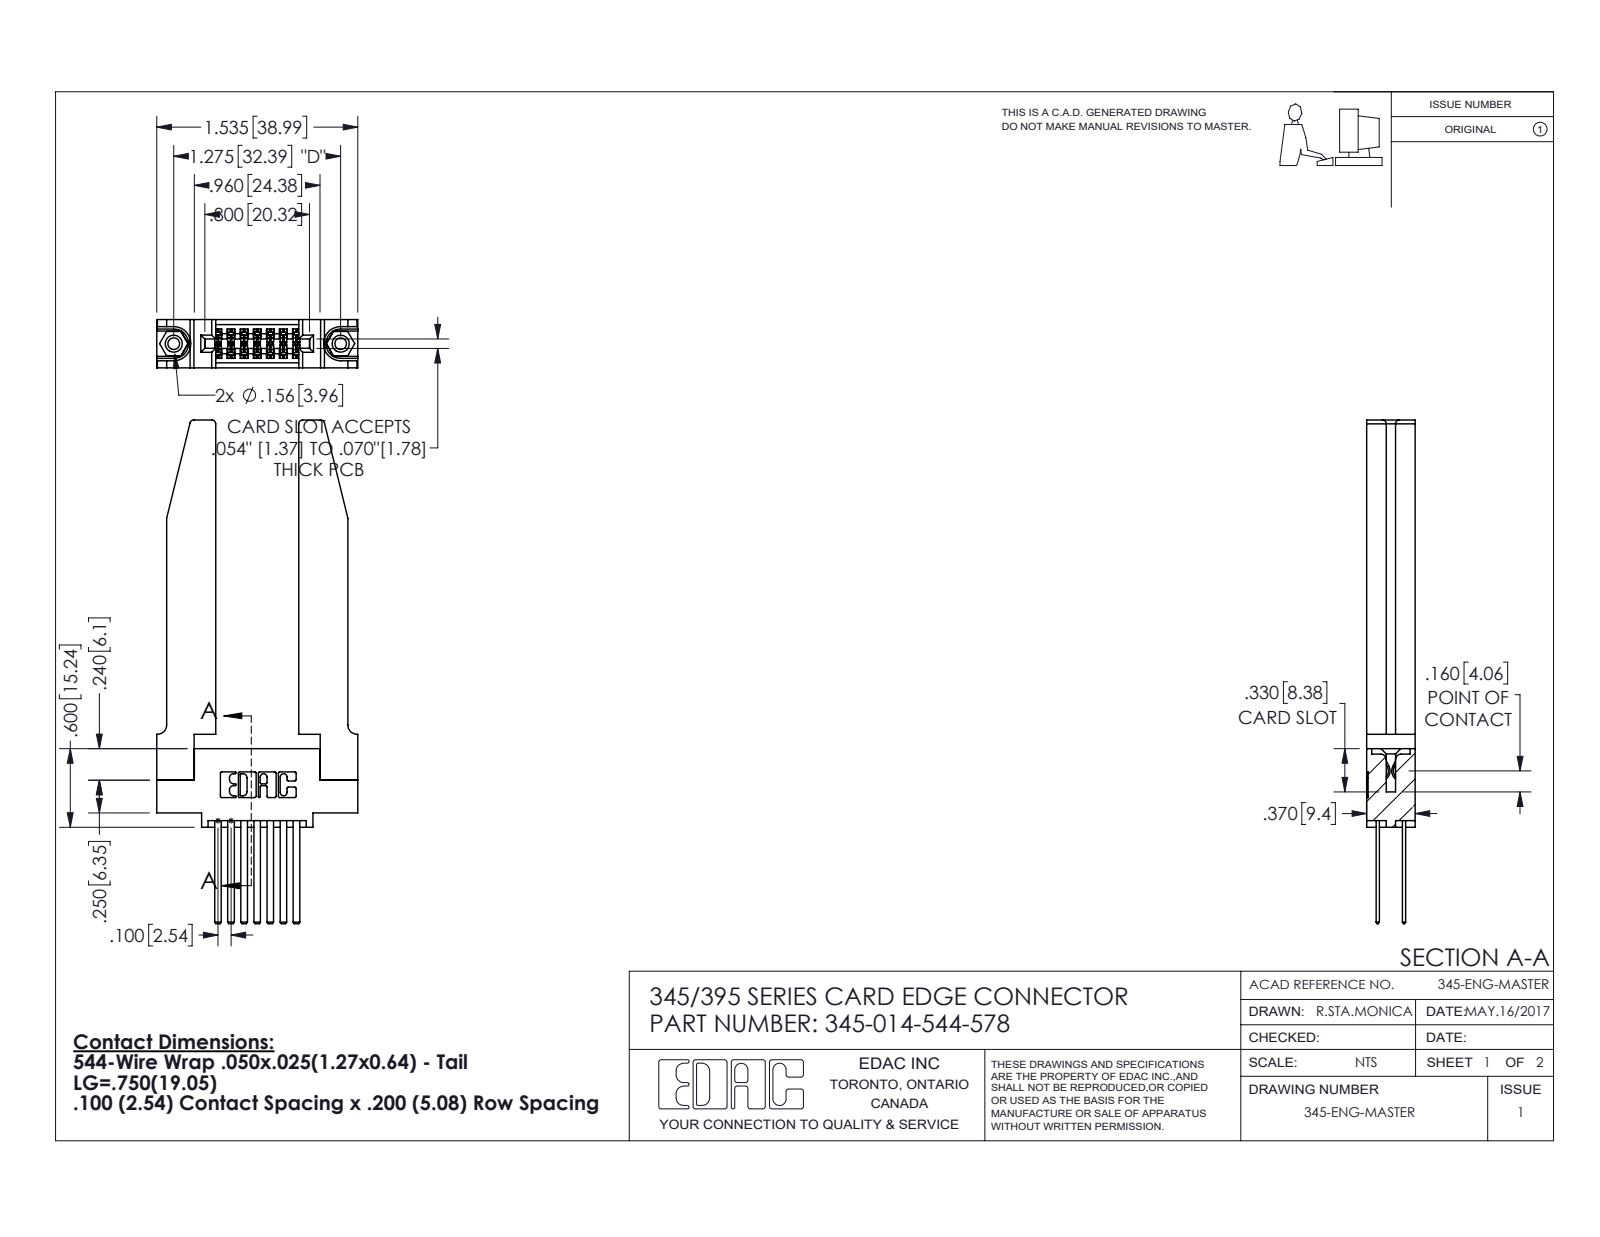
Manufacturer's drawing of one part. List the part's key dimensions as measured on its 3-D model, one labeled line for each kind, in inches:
Part name (STEP PRODUCT): 345-250-001_345-250-001-102; 345 Part_0.110 Offset - 0.156 Dia-TH; 345-014-544-578; 345-220-078_345-220-078 (+1 more)
STEP written by: SolidWorks 2016 (CONFIG_CONTROL_DESIGN)
Units: inches
Bodies: 19 solids, 980 faces (632 planar, 296 cylindrical, 52 other)
Overall size (bounding box): 3.847 × 1.536 × 0.37
Volume: 0.693 in³ · Surface area: 18.8 in²
Round holes (diameter × count): ⌀0.089 ×2, ⌀0.125 ×2, ⌀0.156 ×2, ⌀0.064 ×1
Round bosses / shafts (diameter × count): ⌀0.155 ×2
Partial cylindrical surfaces — rounded edges, fillets, slot ends (radius × count): R0.01 ×22, R0.006 ×21, R0.03 ×8, R0.007 ×6, R0.031 ×6, R0.026 ×3, R0.014 ×2, R0.019 ×2
Main face-to-face distances: 0.37, 0.072, 0.298, 0.098, 0.272, 0.025, 0.2, 0.15, 0.148, 0.22
Hole centre spacings: 0.27, 1.045, 1.275
